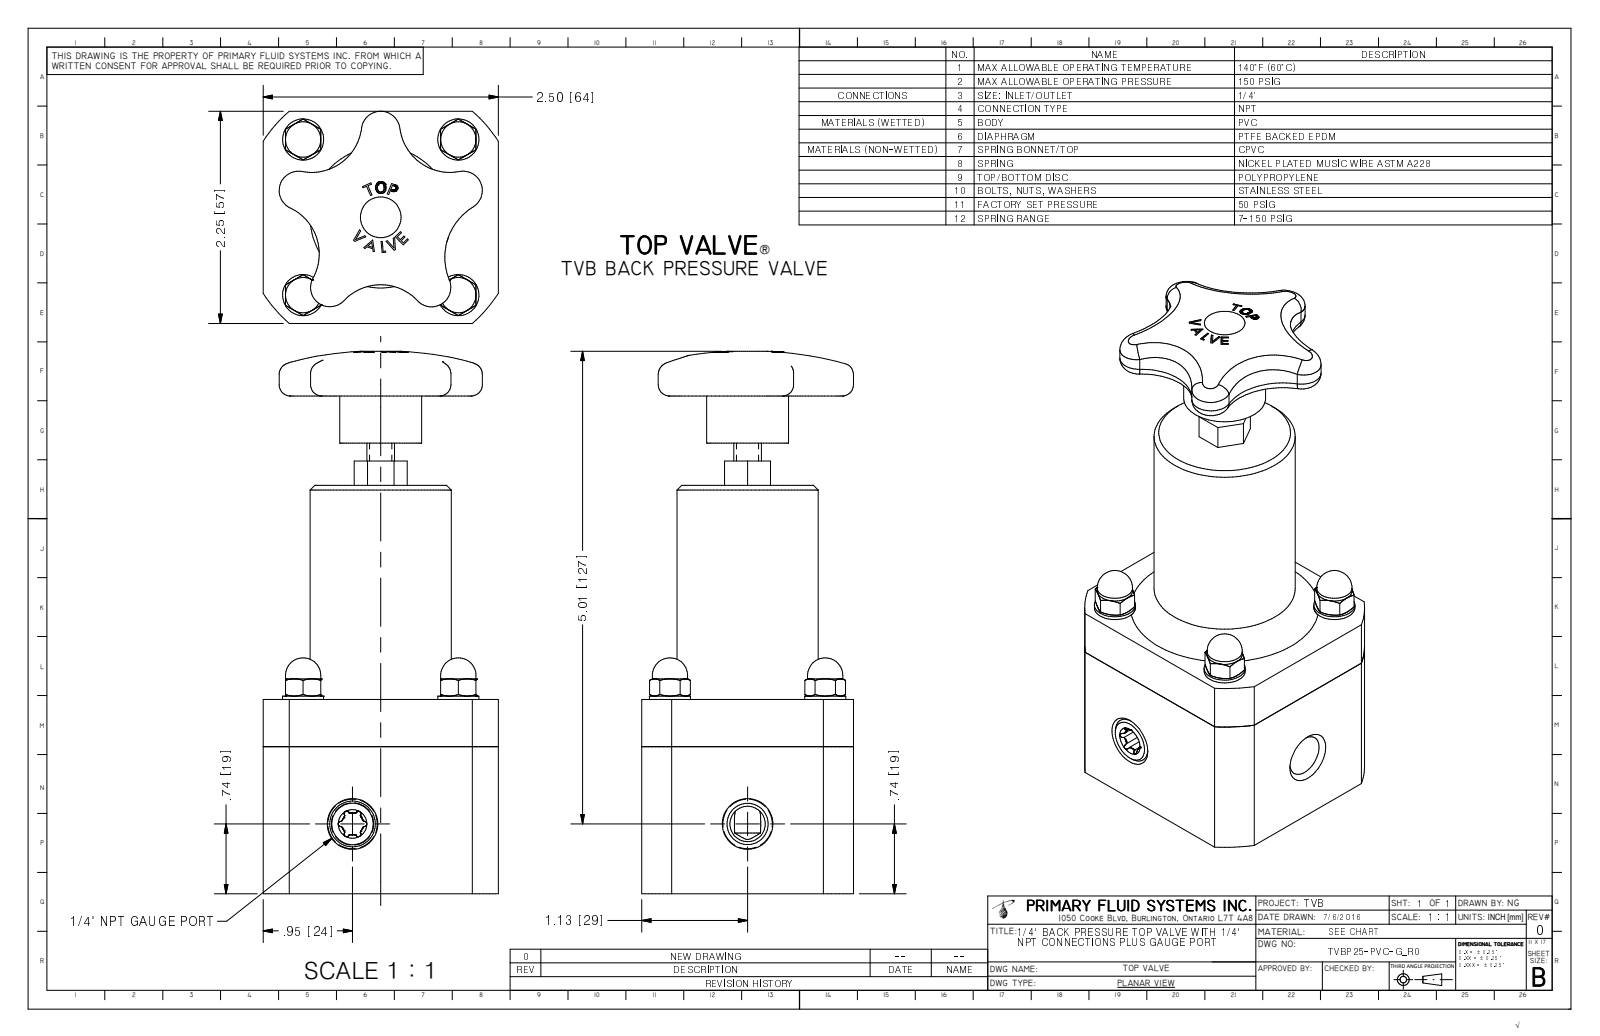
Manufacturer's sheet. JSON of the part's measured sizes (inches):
{"part_name": "TVBP25-PVC-G_R0", "step_written_by": "Autodesk Inventor 2009 (AUTOMOTIVE_DESIGN)", "units": "inches", "bodies": {"solids": 1, "faces": 359, "planar": 148, "cylindrical": 51, "other": 160}, "overall_size": [5.752, 2.5, 2.25], "volume_in3": 16.46, "surface_area_in2": 55.43, "round_holes": [[0.147, 4], [0.437, 1], [0.437, 1]], "round_bosses_or_shafts": [[0.437, 4], [0.375, 4], [0.312, 4], [1.5, 1], [0.87, 1], [0.293, 1]], "partial_cylinders_radius": [[0.027, 6], [0.085, 5], [0.205, 5], [0.536, 4], [0.656, 4], [0.625, 1], [0.745, 1], [1.488, 1]], "face_to_face_distances": [2.25, 2.5, 2.06, 4.33, 2.27, 4.778, 2.718, 0.448, 0.6, 1.9], "hole_center_spacings": [1.65, 1.65, 2.333, 2.334]}
